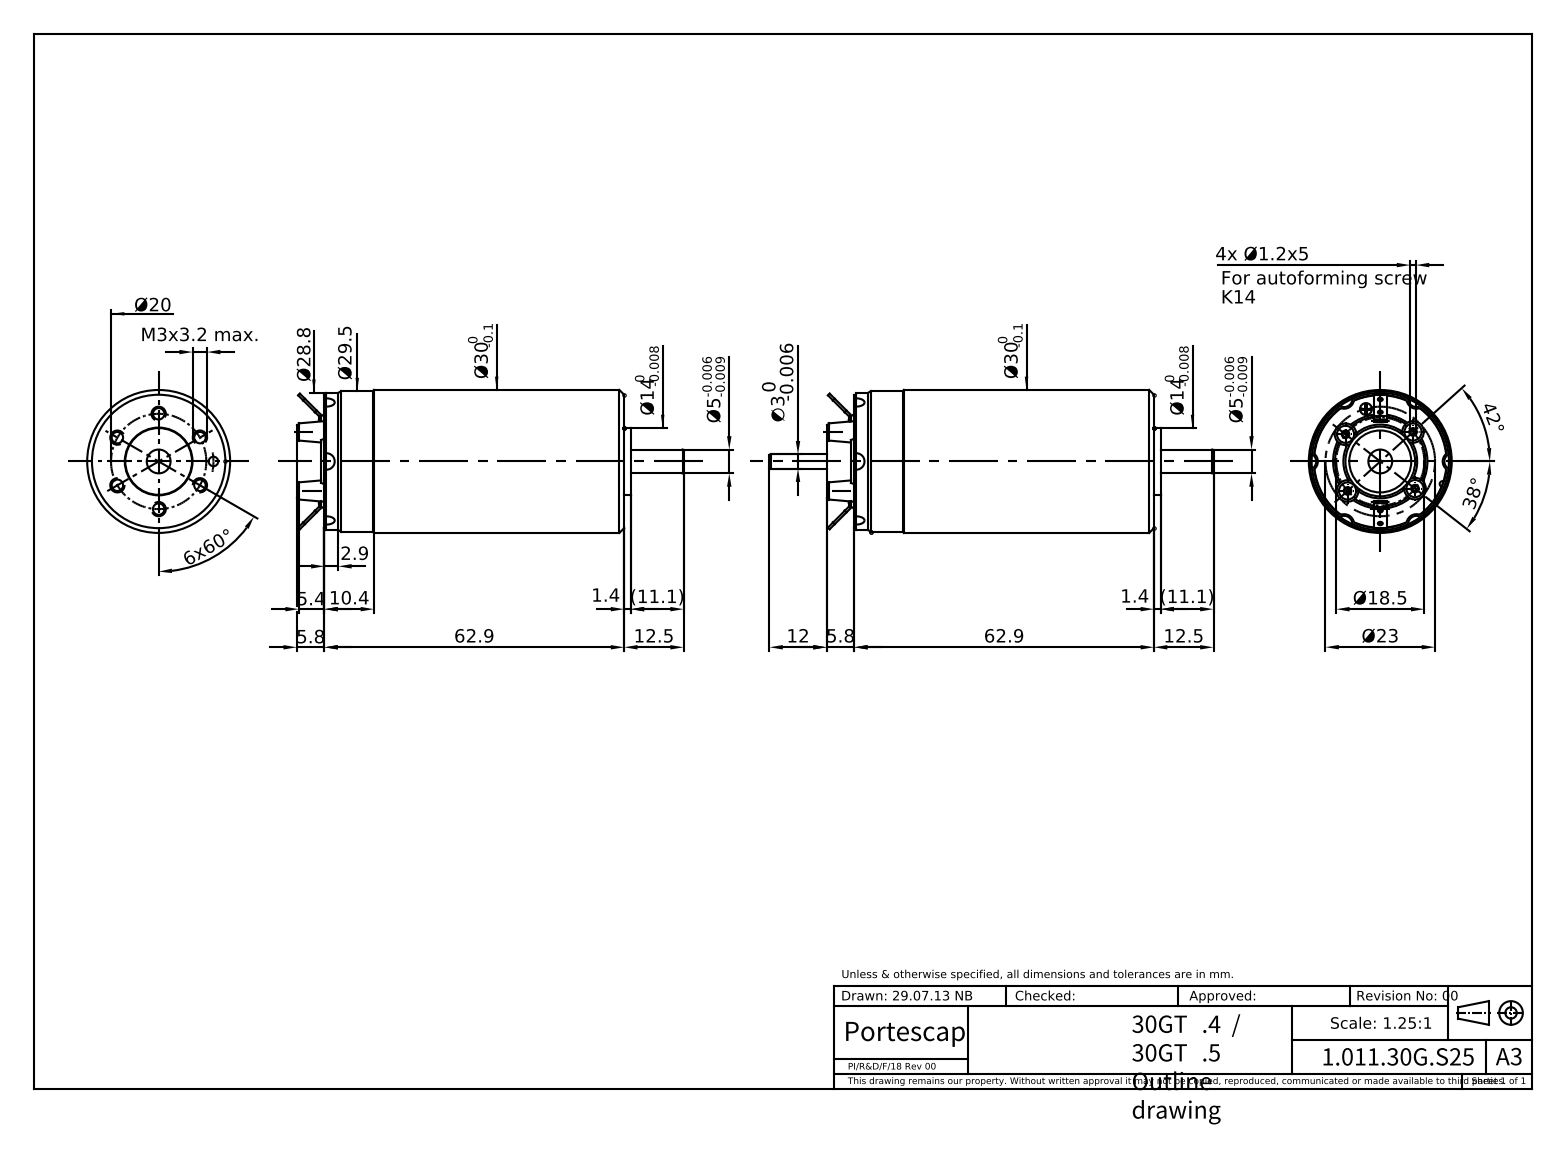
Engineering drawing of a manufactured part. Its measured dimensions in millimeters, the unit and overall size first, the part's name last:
Units: millimetres
Overall size (bounding box): 81.6 × 30 × 30
Round holes (diameter × count): ⌀2.5 ×7, ⌀1.6 ×6, ⌀1 ×4, ⌀1.2 ×4, ⌀2 ×1, ⌀5 ×1, ⌀13 ×1
Round bosses / shafts (diameter × count): ⌀30 ×1, ⌀29.5 ×1, ⌀28.8 ×1, ⌀14 ×1
Partial cylindrical surfaces — rounded edges, fillets, slot ends (radius × count): R2.1 ×6, R0.2 ×4, R0.6 ×1, R13.9 ×1
Main face-to-face distances: 62.9, 68.5, 5.6, 1.4, 64.3, 69.9, 0.4, 0.7, 1.1, 5.8
Hole centre spacings: 10, 17.32, 9.25, 20, 1.54, 2.15, 3.5, 5.02
Volume: 45 622 mm³ · Surface area: 8 590 mm²
Bodies: 1 solid, 180 faces (56 planar, 78 cylindrical, 46 other)
Part name (STEP PRODUCT): 30GT2R82234E_4
STEP written by: PRO/ENGINEER BY PARAMETRIC TECHNOLOGY CORPORATION, 2014310 (CONFIG_CONTROL_DESIGN)
